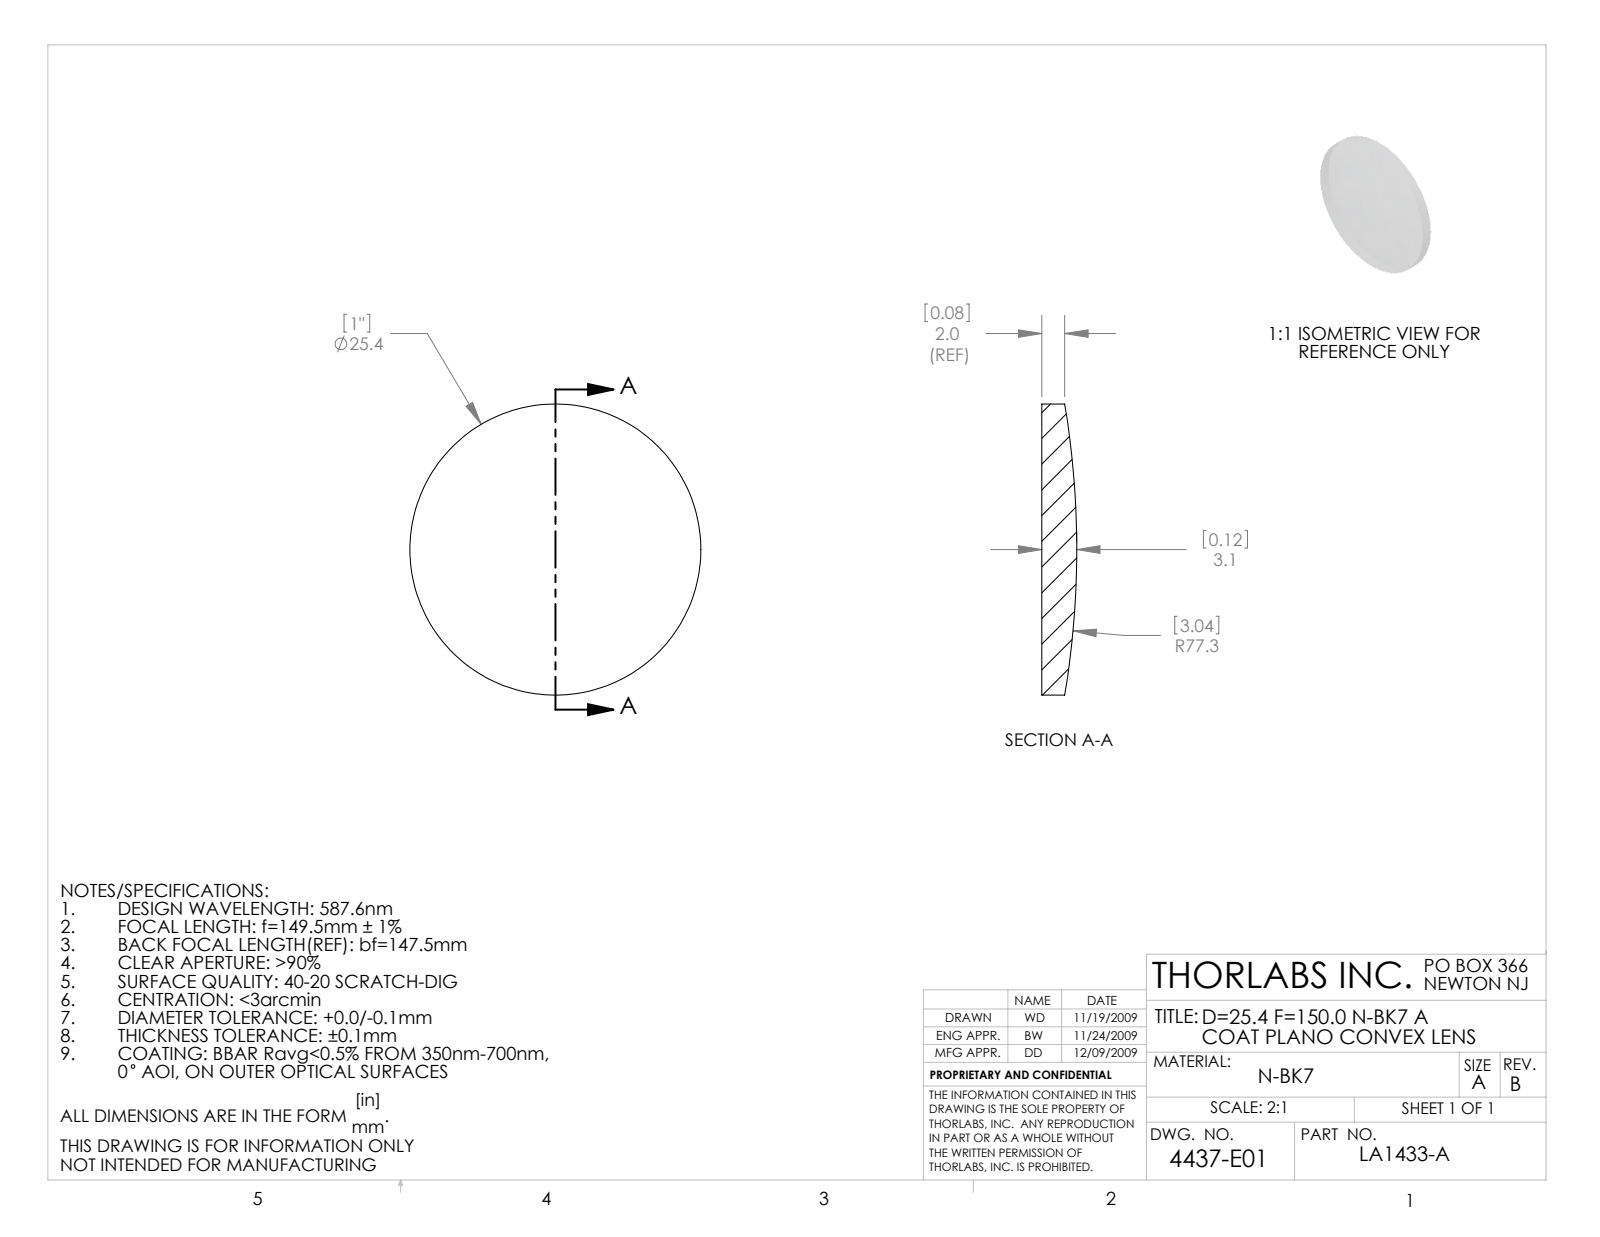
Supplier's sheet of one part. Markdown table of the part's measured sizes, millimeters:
| quantity | value |
| --- | --- |
| part name | 4437-E0W |
| STEP written by | SolidWorks 2009 (AUTOMOTIVE_DESIGN) |
| units | millimeters |
| bodies | 1 solid, 5 faces (1 planar, 2 cylindrical, 2 other) |
| overall size | 25.4 × 25.4 × 3.05 |
| volume | 1 280 mm³ |
| surface area | 1 176 mm² |
| round bosses / shafts (diameter × count) | 25.4 × 1 |
